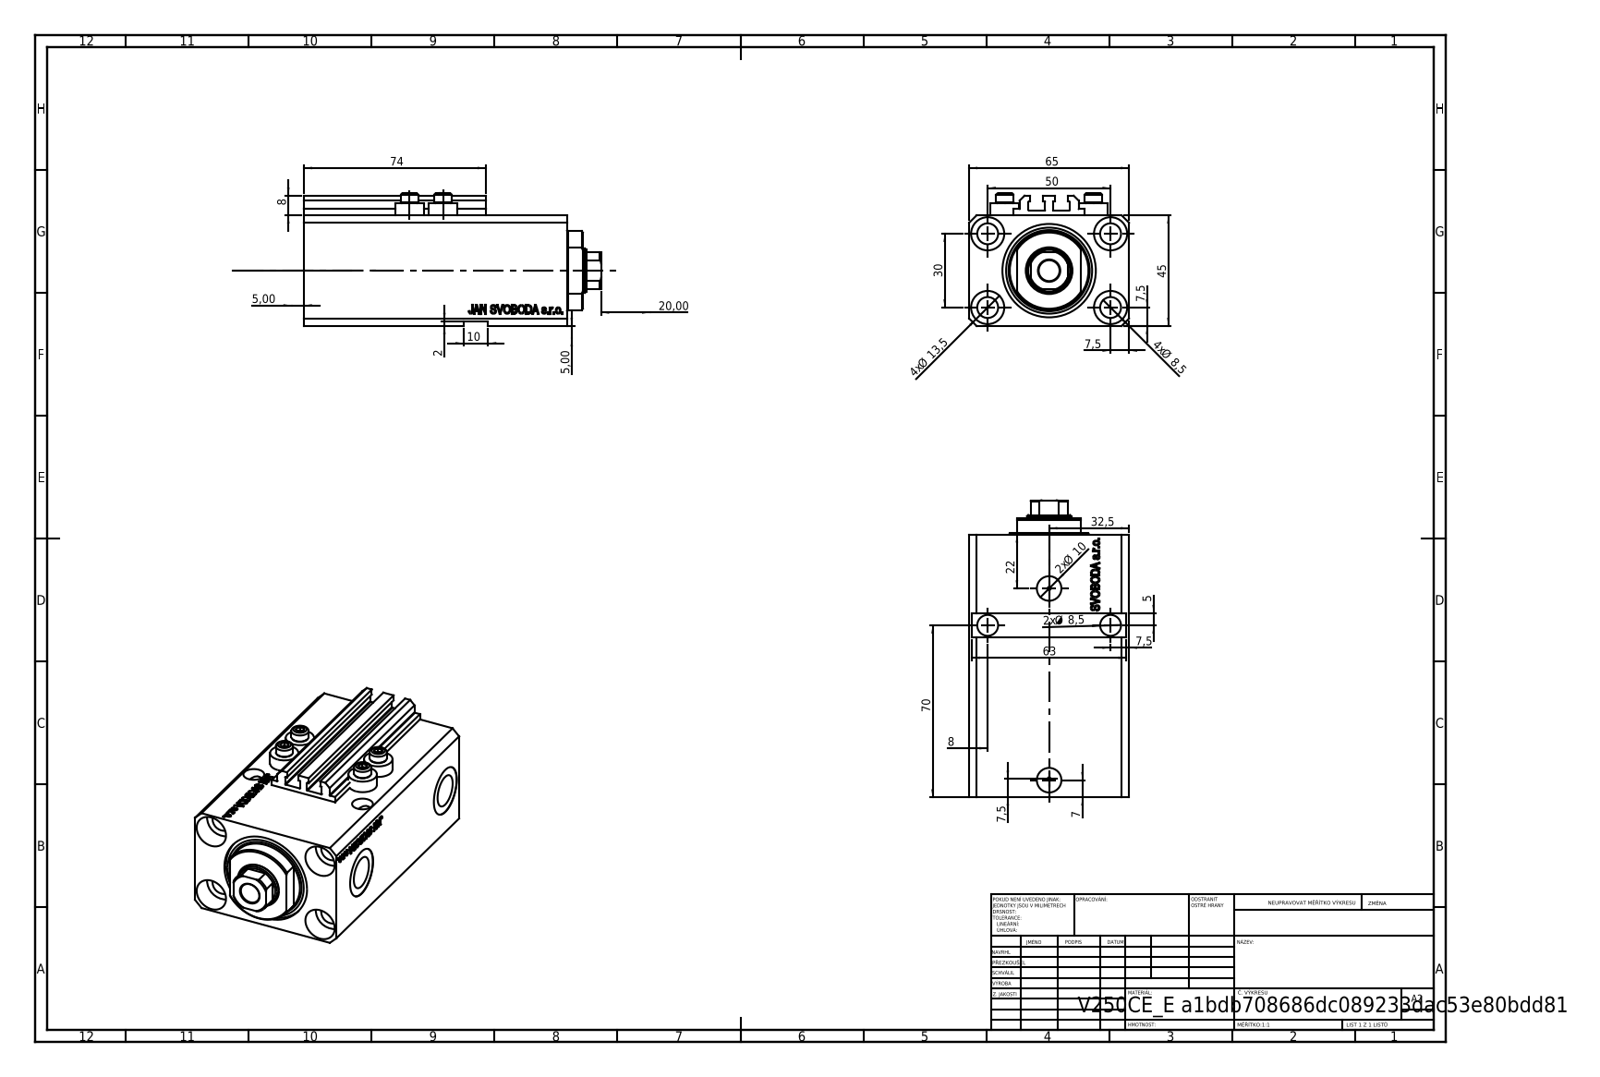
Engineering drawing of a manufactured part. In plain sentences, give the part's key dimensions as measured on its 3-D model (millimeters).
The part is named "V250CE_VC_E; V250CE_C_VCP; ALLEN BOLT V250CE; V250CE_E_Body". Its 3-D file was written by "SolidWorks 2019 (CONFIG_CONTROL_DESIGN)". It is 8 solids with 1067 faces: 511 planar, 126 cylindrical and 430 other. Overall it measures 120.9 by 65 by 54 millimeters. Its volume is 276 859 cubic millimeters and its surface area 77 961 square millimeters. Round holes: 7 of diameter 8.5, 4 of diameter 1.25, 4 of diameter 4, 4 of diameter 13.5, 2 of diameter 10, 2 of diameter 13.16, 2 of diameter 20, 1 of diameter 18, 1 of diameter 25, 1 of diameter 38. Round bosses or shafts: 4 of diameter 11.6, 4 of diameter 7. Partial cylindrical surfaces (rounded edges, fillets, slot ends): 10 of radius 0.2, 1 of radius 8.5, 1 of radius 16. The main face-to-face distances are 45, 65, 81.9, 2, 47, 107, 25.1, 2.5, 6.9, 75. The hole center spacings are 29.15, 50, 13.6, 15.12, 27.89, 30, 33.62, 36.
